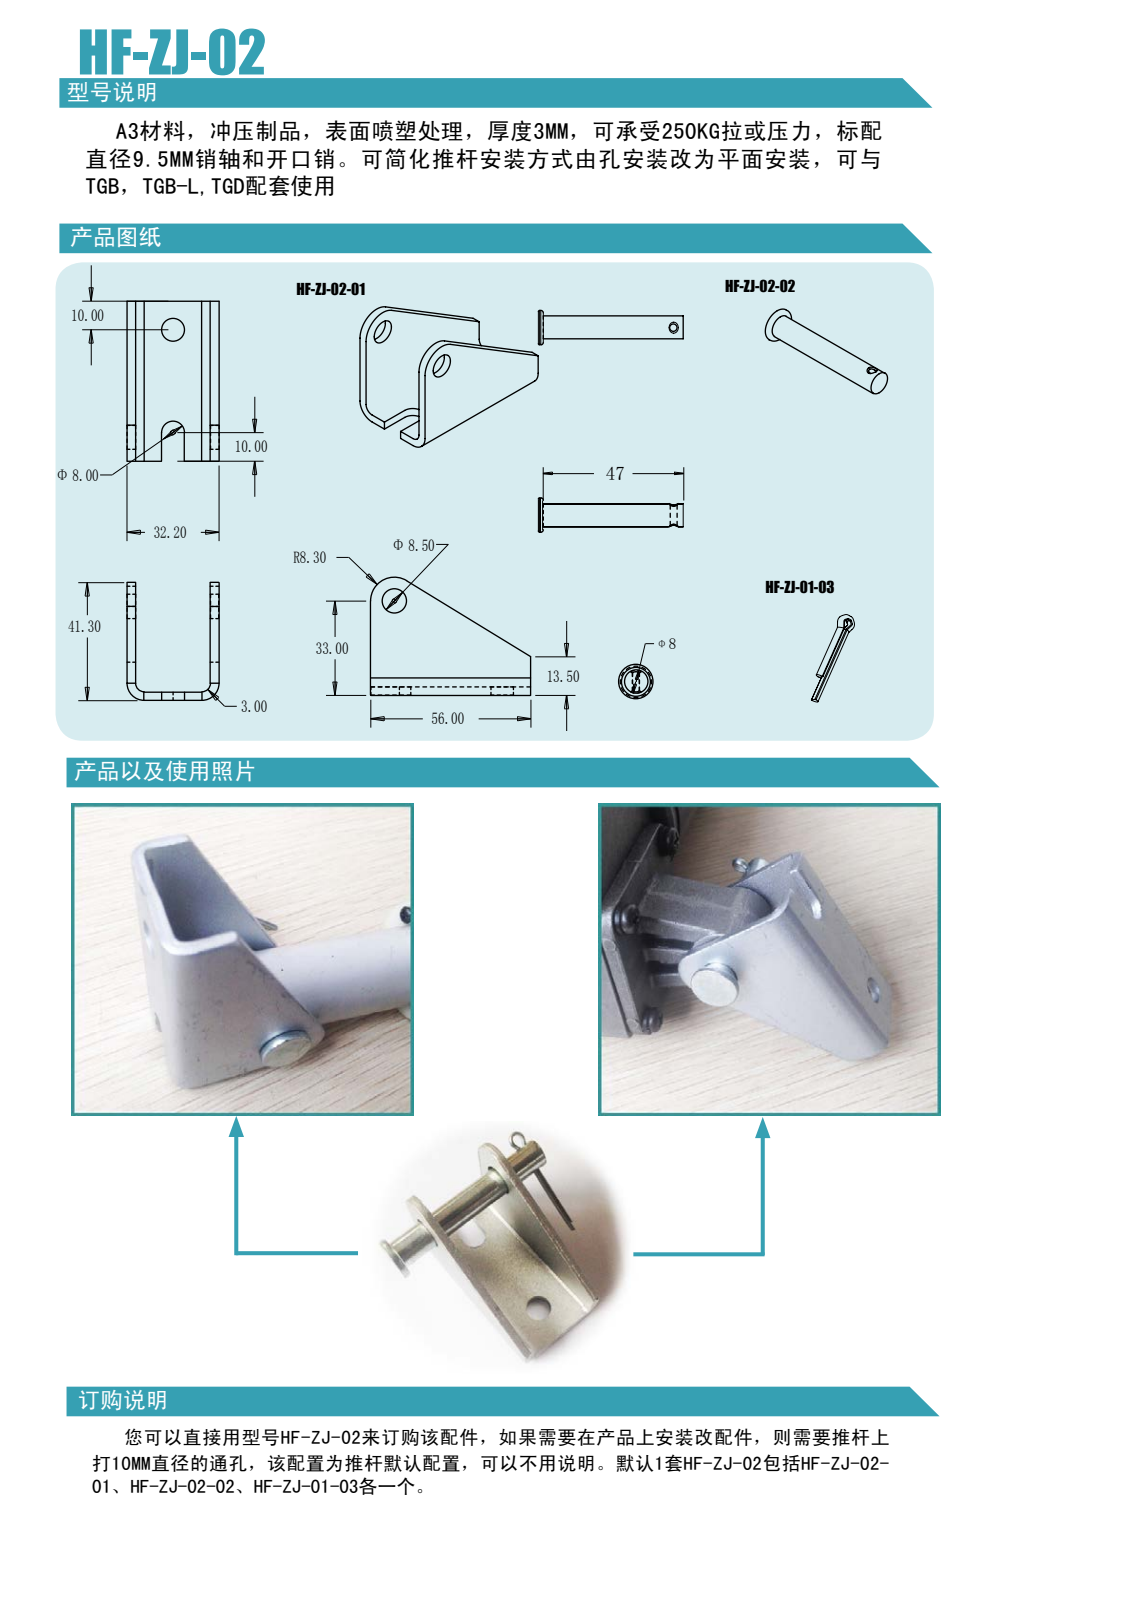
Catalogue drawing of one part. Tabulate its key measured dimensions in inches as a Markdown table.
| quantity | value |
| --- | --- |
| part name | ZJ-02 |
| STEP written by | PRO/ENGINEER BY PARAMETRIC TECHNOLOGY CORPORATION, 2008380 (CONFIG_CONTROL_DESIGN) |
| units | inches |
| bodies | 1 solid, 34 faces (21 planar, 13 cylindrical, 0 other) |
| overall size | 56 × 41.3 × 32.2 |
| volume | 12 948 in³ |
| surface area | 9 765 in² |
| round holes (diameter × count) | 8 × 1, 8.5 × 1 |
| partial cylindrical surfaces (radius × count) | 3 × 2, 6 × 2, 4 × 1, 8.3 × 1 |
| main face-to-face distances | 3, 29.2, 26.2, 32.2, 56, 12.1, 20.1, 9.1, 17.1, 8 |
